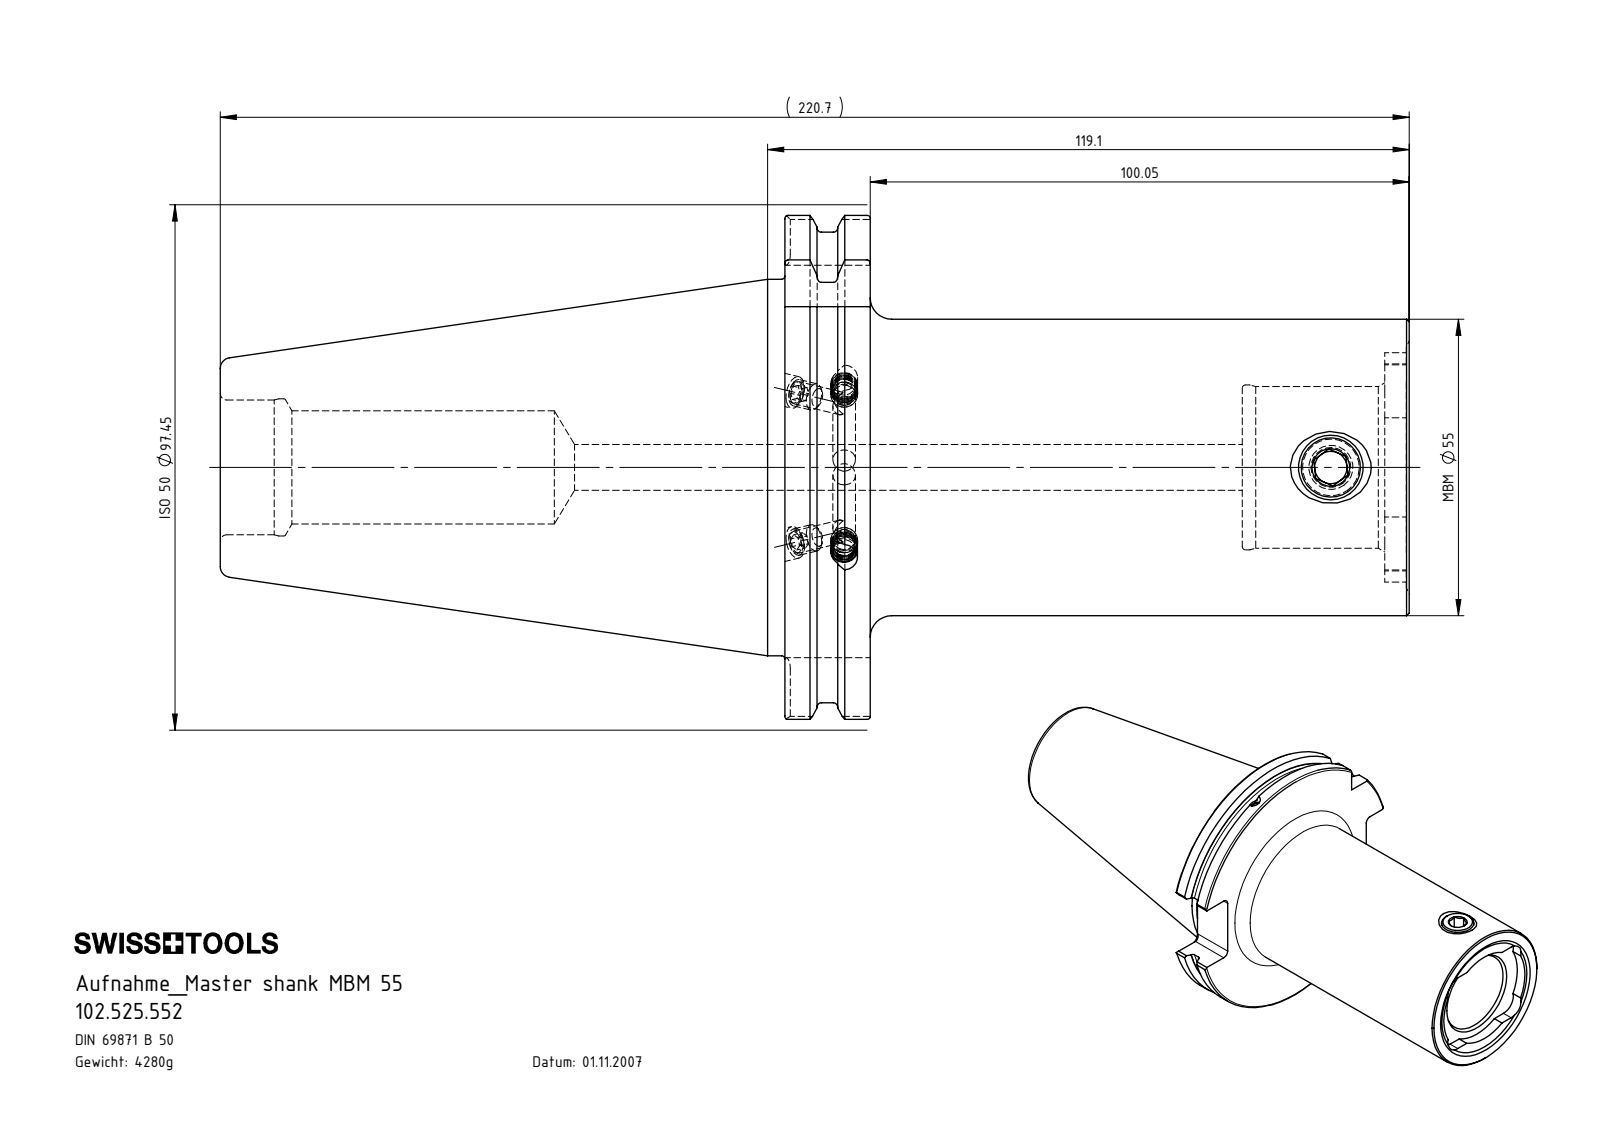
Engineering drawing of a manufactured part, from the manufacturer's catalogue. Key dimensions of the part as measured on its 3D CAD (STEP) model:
Part name (STEP PRODUCT): SB5-MB5.K01.119_D_mit Bundkhlung; ISO 4026 - M5 x 5_PreviewCfg; KVT_MB_600_050; 102.525.552 (+1 more)
STEP written by: SolidWorks 2017 (CONFIG_CONTROL_DESIGN)
Units: millimetres
Bodies: 8 solids, 297 faces (79 planar, 82 cylindrical, 136 other)
Overall size (bounding box): 220.7 × 97.45 × 93.51
Volume: 545 168 mm³ · Surface area: 66 052 mm²
Round holes (diameter × count): ⌀4.2 ×3, ⌀6 ×3, ⌀4 ×2, ⌀5 ×1, ⌀8.5 ×1, ⌀11 ×1, ⌀21 ×1, ⌀25 ×1, ⌀25.45 ×1, ⌀30 ×1, ⌀30.6 ×1
Round bosses / shafts (diameter × count): ⌀5 ×3, ⌀91 ×1, ⌀69.85 ×1, ⌀55 ×1, ⌀12 ×1
Partial cylindrical surfaces — rounded edges, fillets, slot ends (radius × count): R2 ×8, R5.2 ×4, R18.5 ×1, R21.27 ×1, R48.73 ×1
Main face-to-face distances: 15.85, 84.9, 69.05, 115.9, 100.05, 31, 111.35, 95.5, 26.45, 4.55
